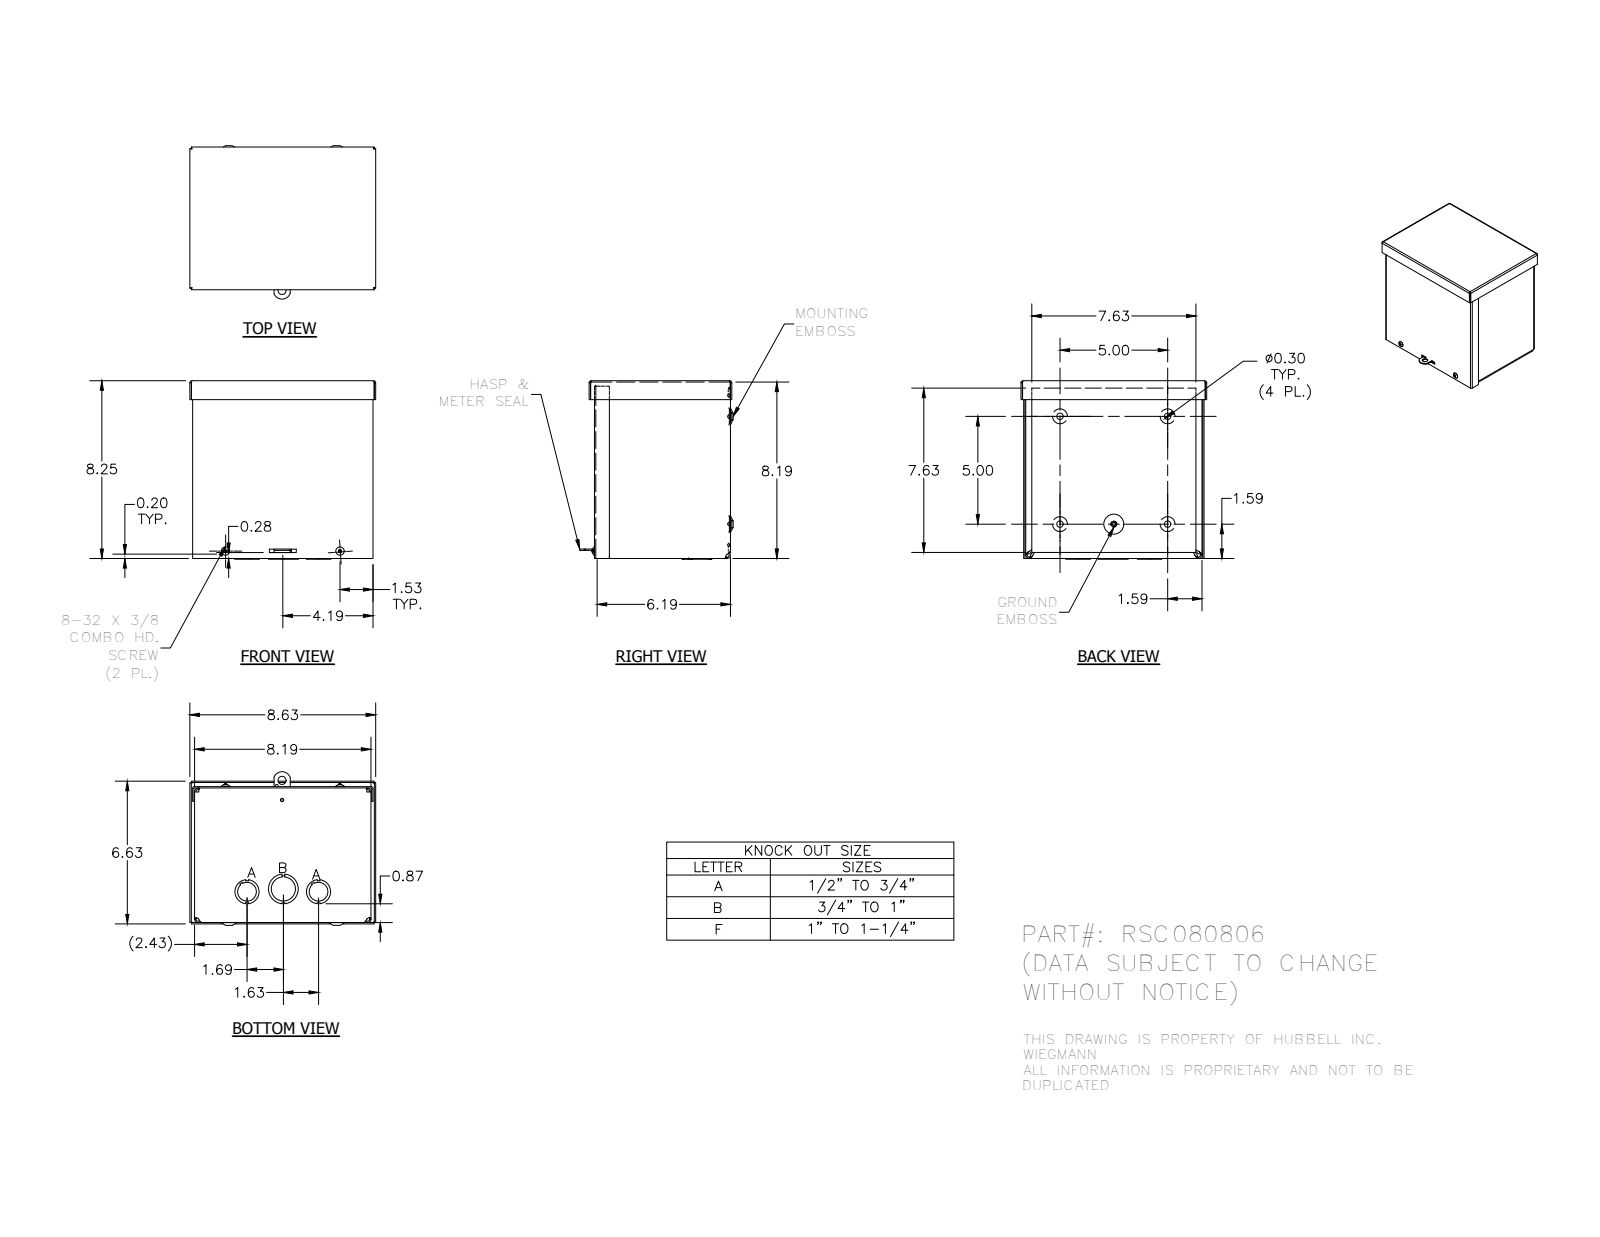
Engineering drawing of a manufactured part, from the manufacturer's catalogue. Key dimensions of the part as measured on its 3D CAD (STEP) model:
Part name (STEP PRODUCT): RSC080806; RSC080806_WRAP; RSC0808_LID; RSC0806_CAP (+4 more)
STEP written by: Autodesk Inventor 2012 (AUTOMOTIVE_DESIGN)
Units: inches
Bodies: 7 solids, 503 faces (238 planar, 121 cylindrical, 144 other)
Overall size (bounding box): 8.625 × 8.281 × 7.125
Volume: 28.55 in³ · Surface area: 935 in²
Round holes (diameter × count): ⌀0.3 ×4, ⌀0.313 ×4, ⌀1.125 ×3, ⌀0.125 ×2, ⌀0.148 ×2, ⌀0.875 ×2, ⌀0.156 ×1, ⌀0.165 ×1, ⌀0.375 ×1, ⌀1.375 ×1
Round bosses / shafts (diameter × count): ⌀0.384 ×2, ⌀0.164 ×2, ⌀0.229 ×1
Partial cylindrical surfaces — rounded edges, fillets, slot ends (radius × count): R0.01 ×10, R0.031 ×8, R0.093 ×8, R0.125 ×8, R0.187 ×8, R0.021 ×4, R0.031 ×4, R0.055 ×4
Main face-to-face distances: 0.062, 8.126, 0.062, 8.188, 6.249, 0.124, 6.187, 0.063, 6.312, 6.25
Hole centre spacings: 5, 1.072, 1.261, 2.5, 5.313, 5.59, 6.063, 6.253
